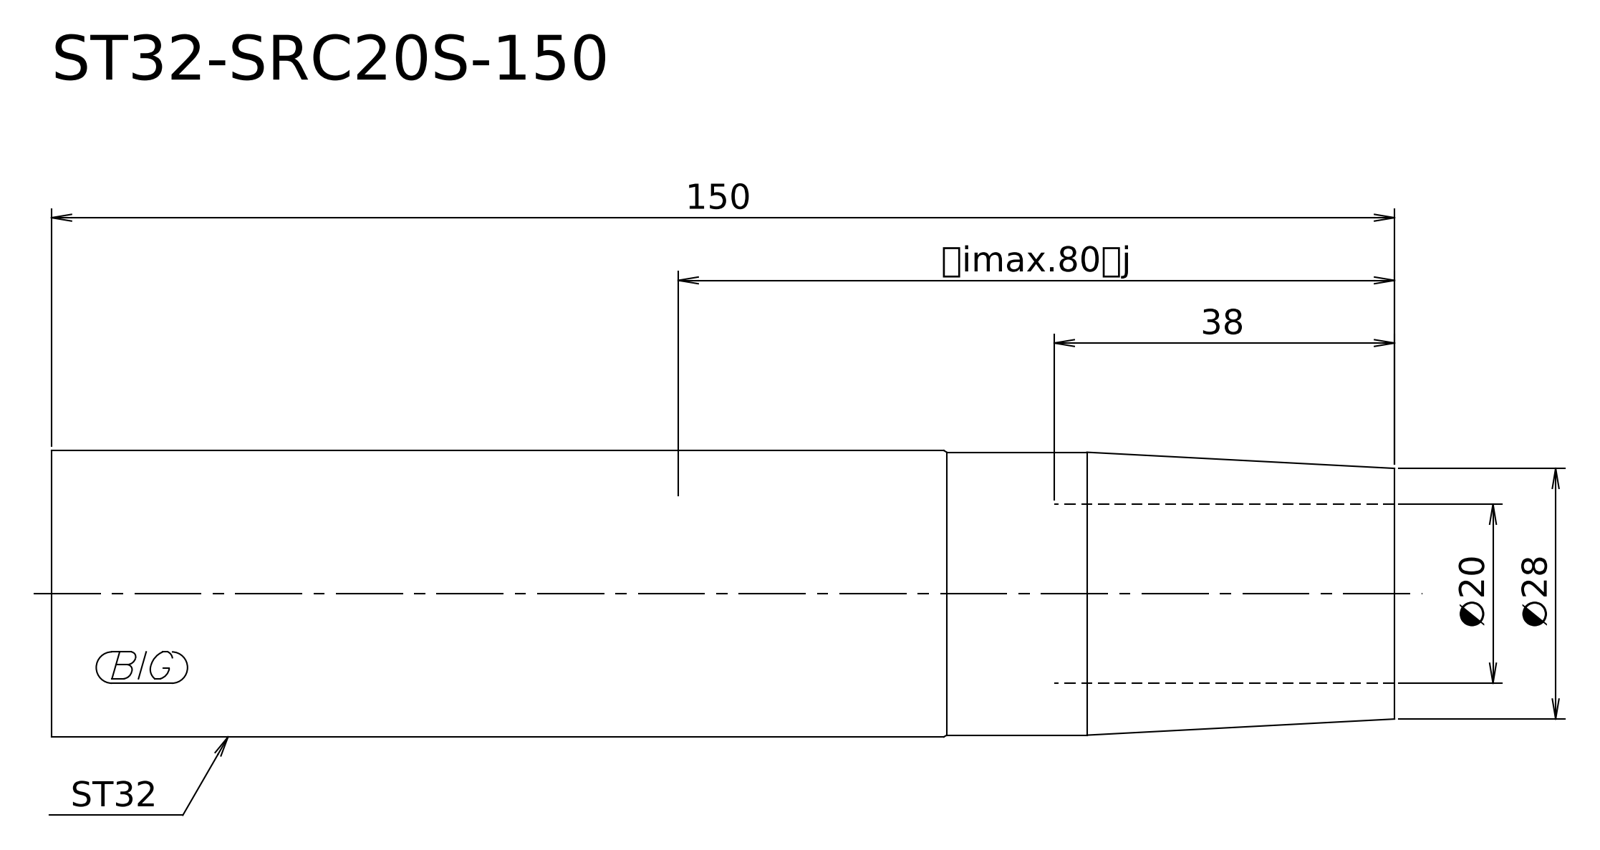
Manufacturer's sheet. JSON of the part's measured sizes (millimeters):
{"step_written_by": "Kubotek KeyCreator V8.5.1 (14335) (CONFIG_CONTROL_DESIGN)", "units": "millimeters", "bodies": {"solids": 1, "faces": 6, "planar": 2, "cylindrical": 2, "other": 2}, "overall_size": [150, 32, 32], "volume_mm3": 116682, "surface_area_mm2": 16252, "round_bosses_or_shafts": [[32, 1], [31.6, 1]], "face_to_face_distances": [150]}
